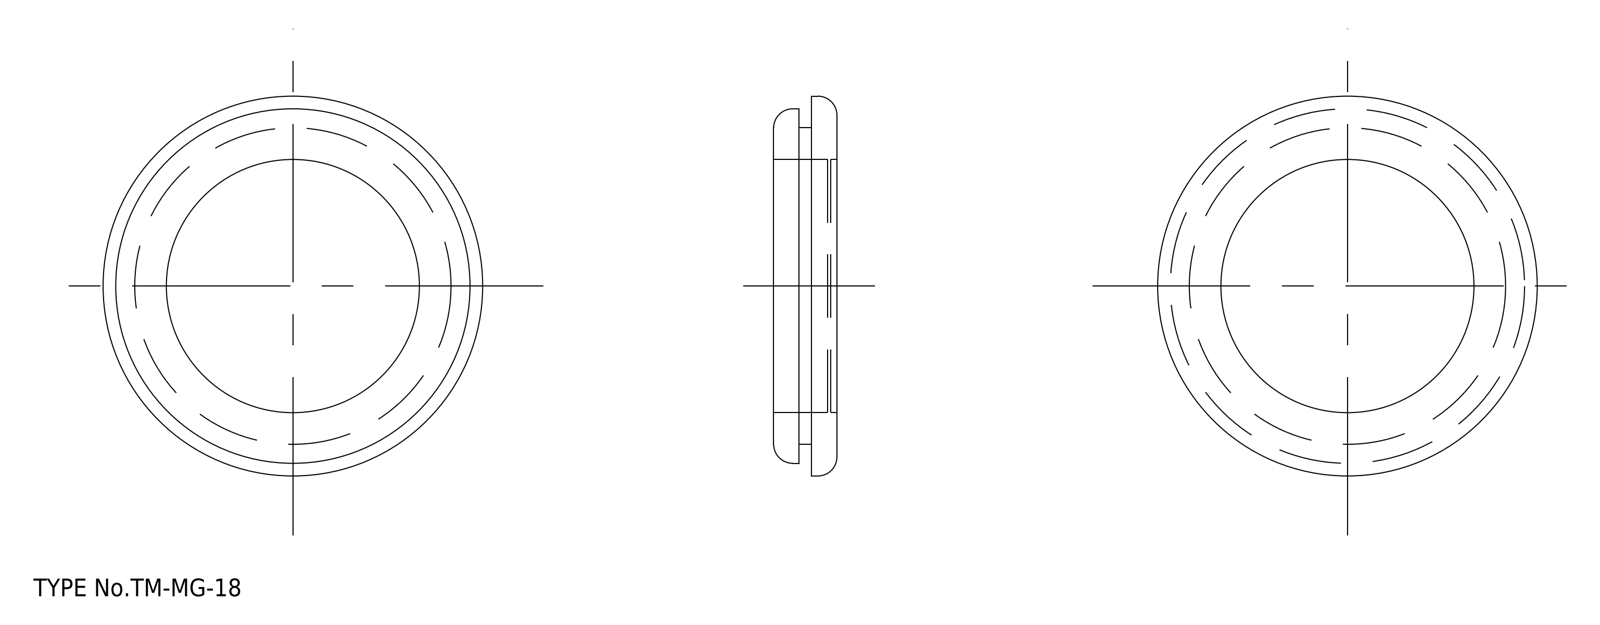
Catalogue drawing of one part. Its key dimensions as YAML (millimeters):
step_written_by: "spGate 17.5.1 (AUTOMOTIVE_DESIGN)"
units: millimeters
bodies: {solids: 1, faces: 20, planar: 6, cylindrical: 10, other: 4}
overall_size: [60, 60, 10]
volume: 12471
surface_area: 9145
round_holes:
  - {diameter: 40, count: 1}
round_bosses_or_shafts:
  - {diameter: 60, count: 1}
  - {diameter: 56, count: 1}
  - {diameter: 50, count: 1}
face_to_face_distances: [4, 0.5, 6, 1.5, 1, 2.5, 3, 8.5, 9, 10]
